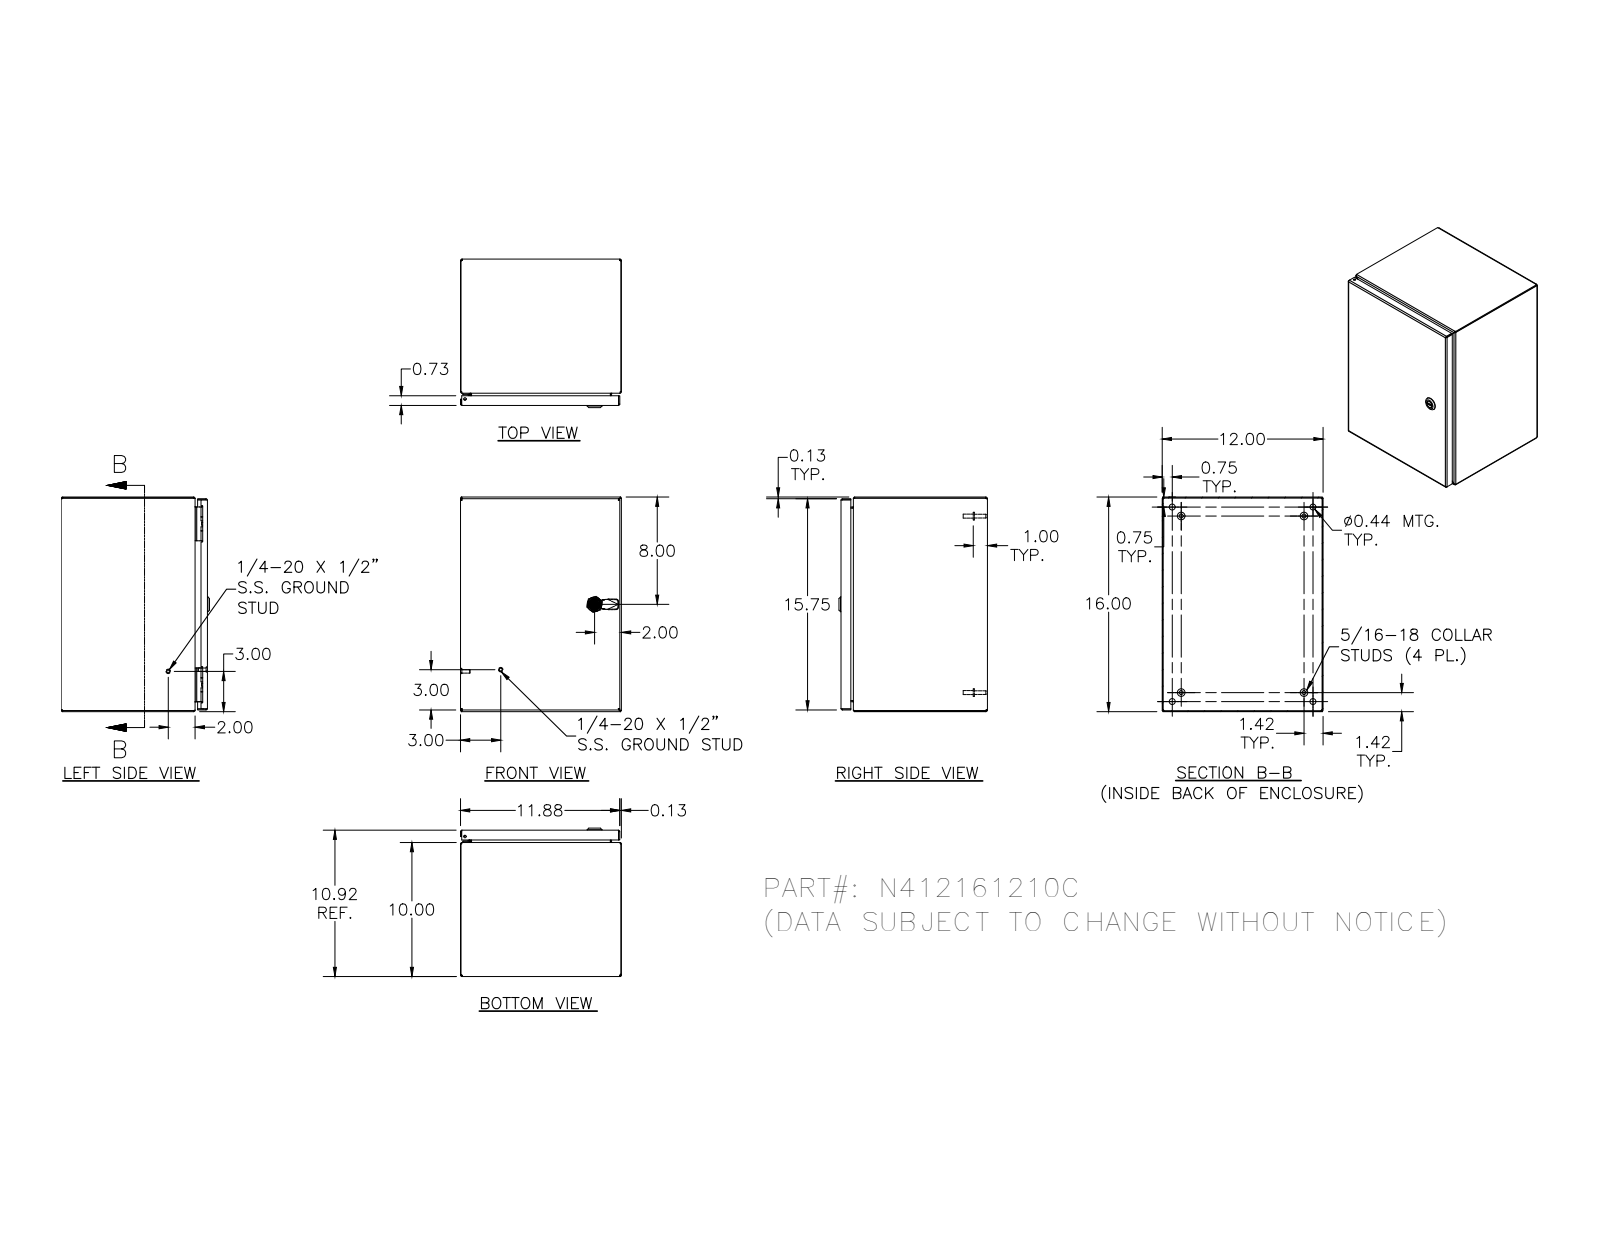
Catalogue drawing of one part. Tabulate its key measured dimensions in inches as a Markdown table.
| quantity | value |
| --- | --- |
| part name | N412161210C |
| STEP written by | SolidWorks 2018 (AUTOMOTIVE_DESIGN) |
| units | inches |
| bodies | 33 solids, 1449 faces (530 planar, 547 cylindrical, 372 other) |
| overall size | 16 × 12 × 11.075 |
| volume | 78.69 in³ |
| surface area | 2 144 in² |
| round holes (diameter × count) | 0.188 × 5, 0.093 × 4, 0.152 × 4, 0.167 × 4, 0.172 × 4, 0.437 × 4, 0.156 × 2, 0.187 × 1, 0.197 × 1, 0.315 × 1, 0.394 × 1, 0.402 × 1 |
| round bosses / shafts (diameter × count) | 0.25 × 10, 0.563 × 4, 0.36 × 4, 0.32 × 4, 0.3 × 4, 0.275 × 4, 0.256 × 4, 0.164 × 4 |
| partial cylindrical surfaces (radius × count) | 0.012 × 30, 0.031 × 30, 0.05 × 26, 0.105 × 20, 0.016 × 18, 0.125 × 16, 0.02 × 13, 0.032 × 8 |
| main face-to-face distances | 0.074, 10.843, 0.074, 10.769, 10.917, 11.926, 12, 11.852, 11.926, 15.852 |
| hole center spacings | 12, 0.66, 0.656, 1.307, 1.965, 0.5, 0.984, 1.311 |
